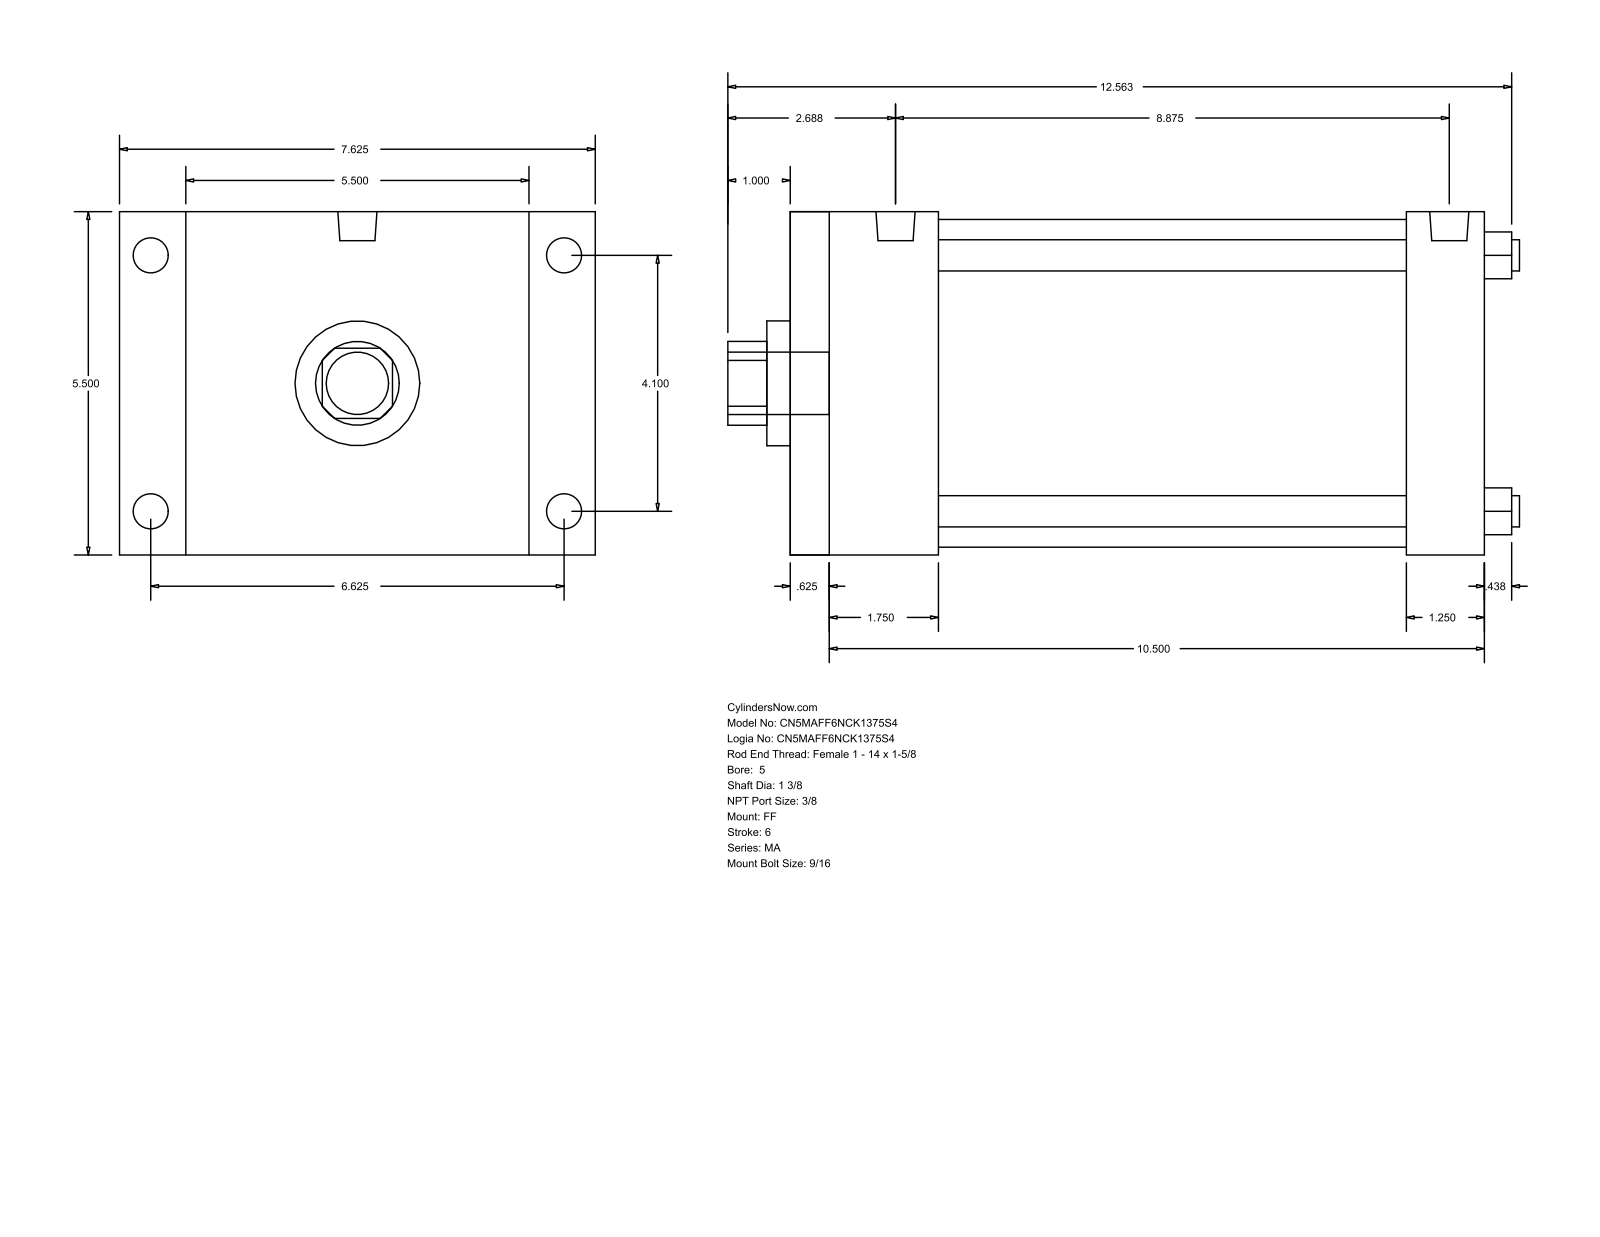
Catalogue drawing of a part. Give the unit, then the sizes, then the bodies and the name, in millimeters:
Units: millimetres
Overall size (bounding box): 322.26 × 193.68 × 139.7
Round holes (diameter × count): ⌀12.7 ×4, ⌀34.92 ×1, ⌀50.8 ×1, ⌀133.35 ×1
Round bosses / shafts (diameter × count): ⌀14.29 ×4, ⌀11.11 ×4, ⌀15.93 ×2, ⌀25.4 ×1
Partial cylindrical surfaces — rounded edges, fillets, slot ends (radius × count): R17.06 ×1
Main face-to-face distances: 139.7, 282.58, 15.87, 266.71, 250.83, 234.96, 31.75, 60.32, 44.45, 190.51
Hole centre spacings: 73.64, 104.14, 147.28
Bodies: 0 solids, 92 faces (64 planar, 28 cylindrical, 0 other)
Part name (STEP PRODUCT): MA_FF__0500_1.375
STEP written by: GSSL Pune (CONFIG_CONTROL_DESIGN)
